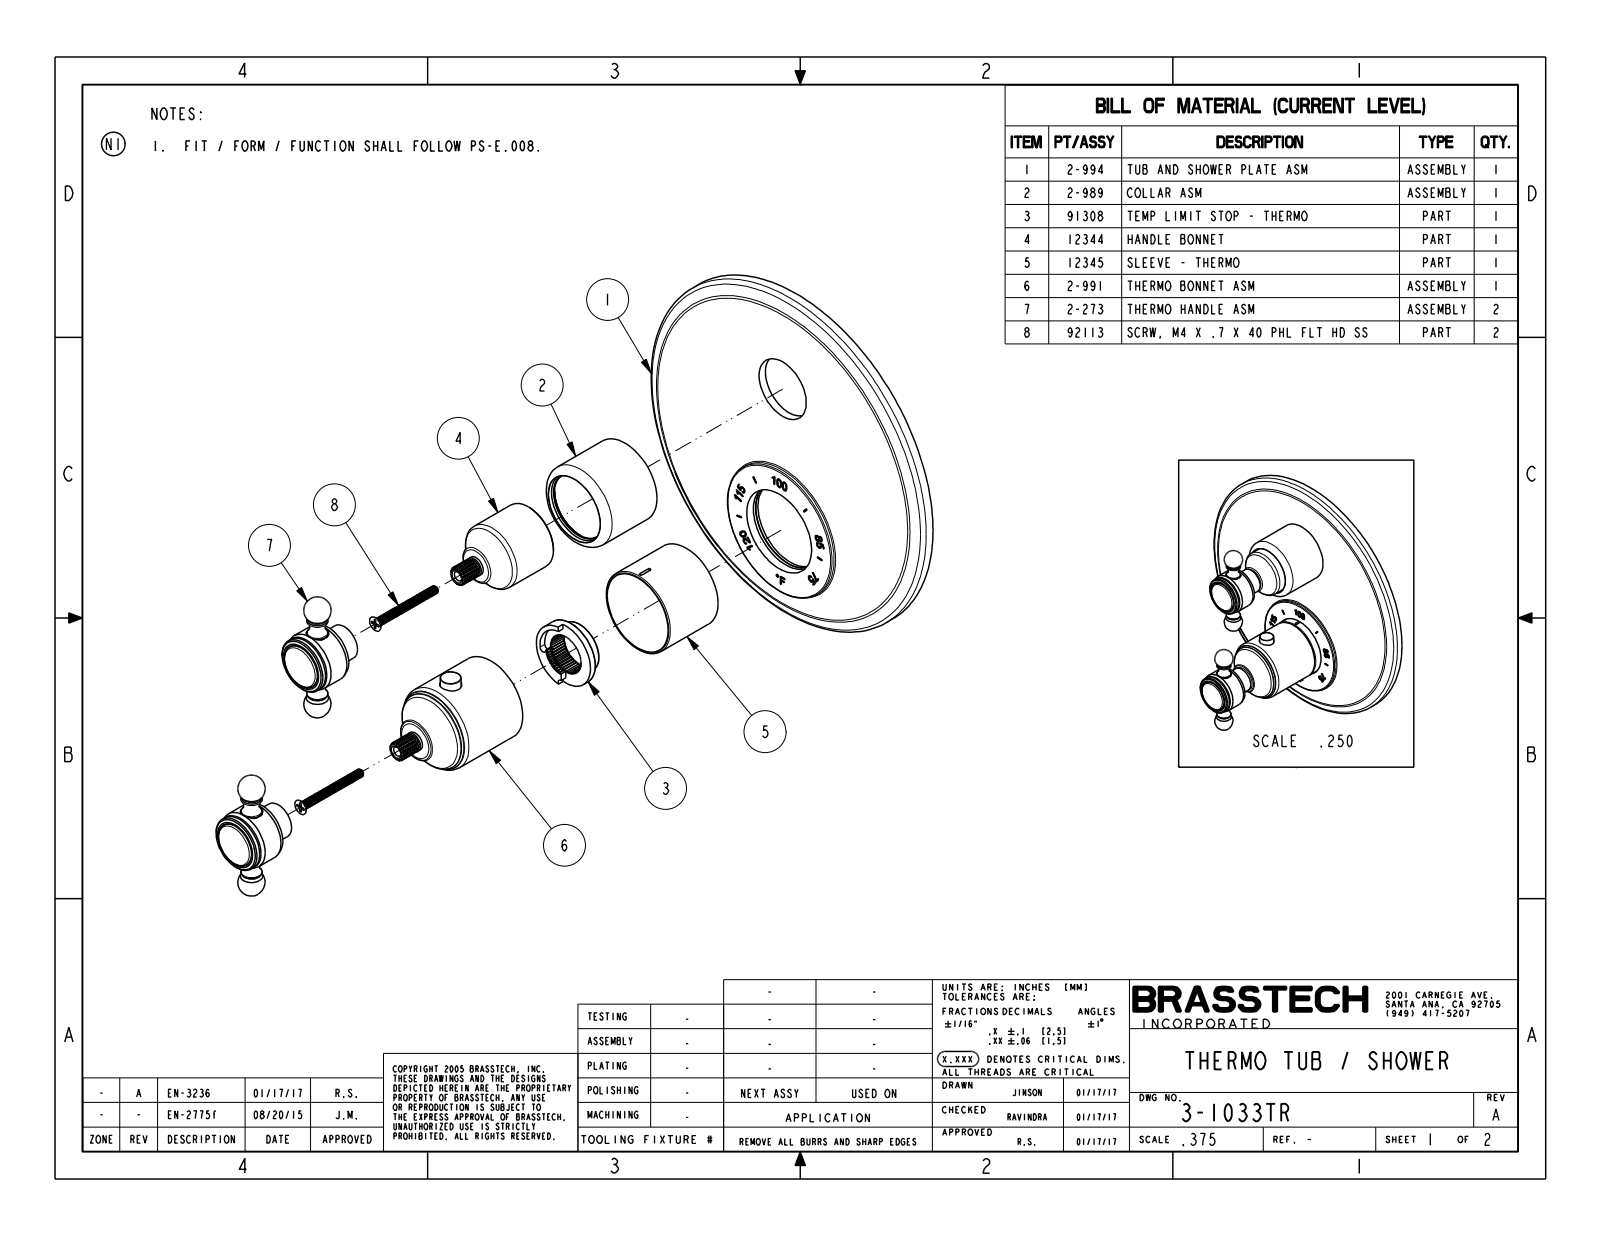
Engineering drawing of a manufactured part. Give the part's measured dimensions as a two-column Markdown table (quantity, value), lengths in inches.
| quantity | value |
| --- | --- |
| part name | 12346_AF4; H-78_2_FEET_AF7; 91678; 2-994_AF4_ASM (+8 more) |
| STEP written by | PRO/ENGINEER BY PARAMETRIC TECHNOLOGY CORPORATION, 2013150 (CONFIG_CONTROL_DESIGN) |
| units | inches |
| bodies | 30 solids, 3017 faces (873 planar, 746 cylindrical, 1398 other) |
| overall size | 7.087 × 7.087 × 4.479 |
| volume | 10.04 in³ |
| surface area | 275.1 in² |
| round holes (diameter × count) | 0.136 × 4, 0.19 × 2, 0.205 × 2, 0.41 × 2, 0.5 × 2, 0.855 × 2, 0.057 × 1, 0.079 × 1, 0.1 × 1, 0.126 × 1, 0.276 × 1, 0.276 × 1 |
| round bosses / shafts (diameter × count) | 0.164 × 4, 0.157 × 3, 1.654 × 2, 1.115 × 2, 1.055 × 2, 0.687 × 2, 0.512 × 2, 0.392 × 2 |
| partial cylindrical surfaces (radius × count) | 0.047 × 3, 0.169 × 3, 0.17 × 3, 0.039 × 2, 0.075 × 2, 0.082 × 2, 0.164 × 2, 0.169 × 2 |
| main face-to-face distances | 0.08, 0.083, 0.163, 0.17, 0.09, 0.253, 0.185, 0.268, 0.348, 0.438 |
| hole center spacings | 1.617, 0.367, 0.554, 1.019, 1.022, 1.293, 1.572, 1.574 |
